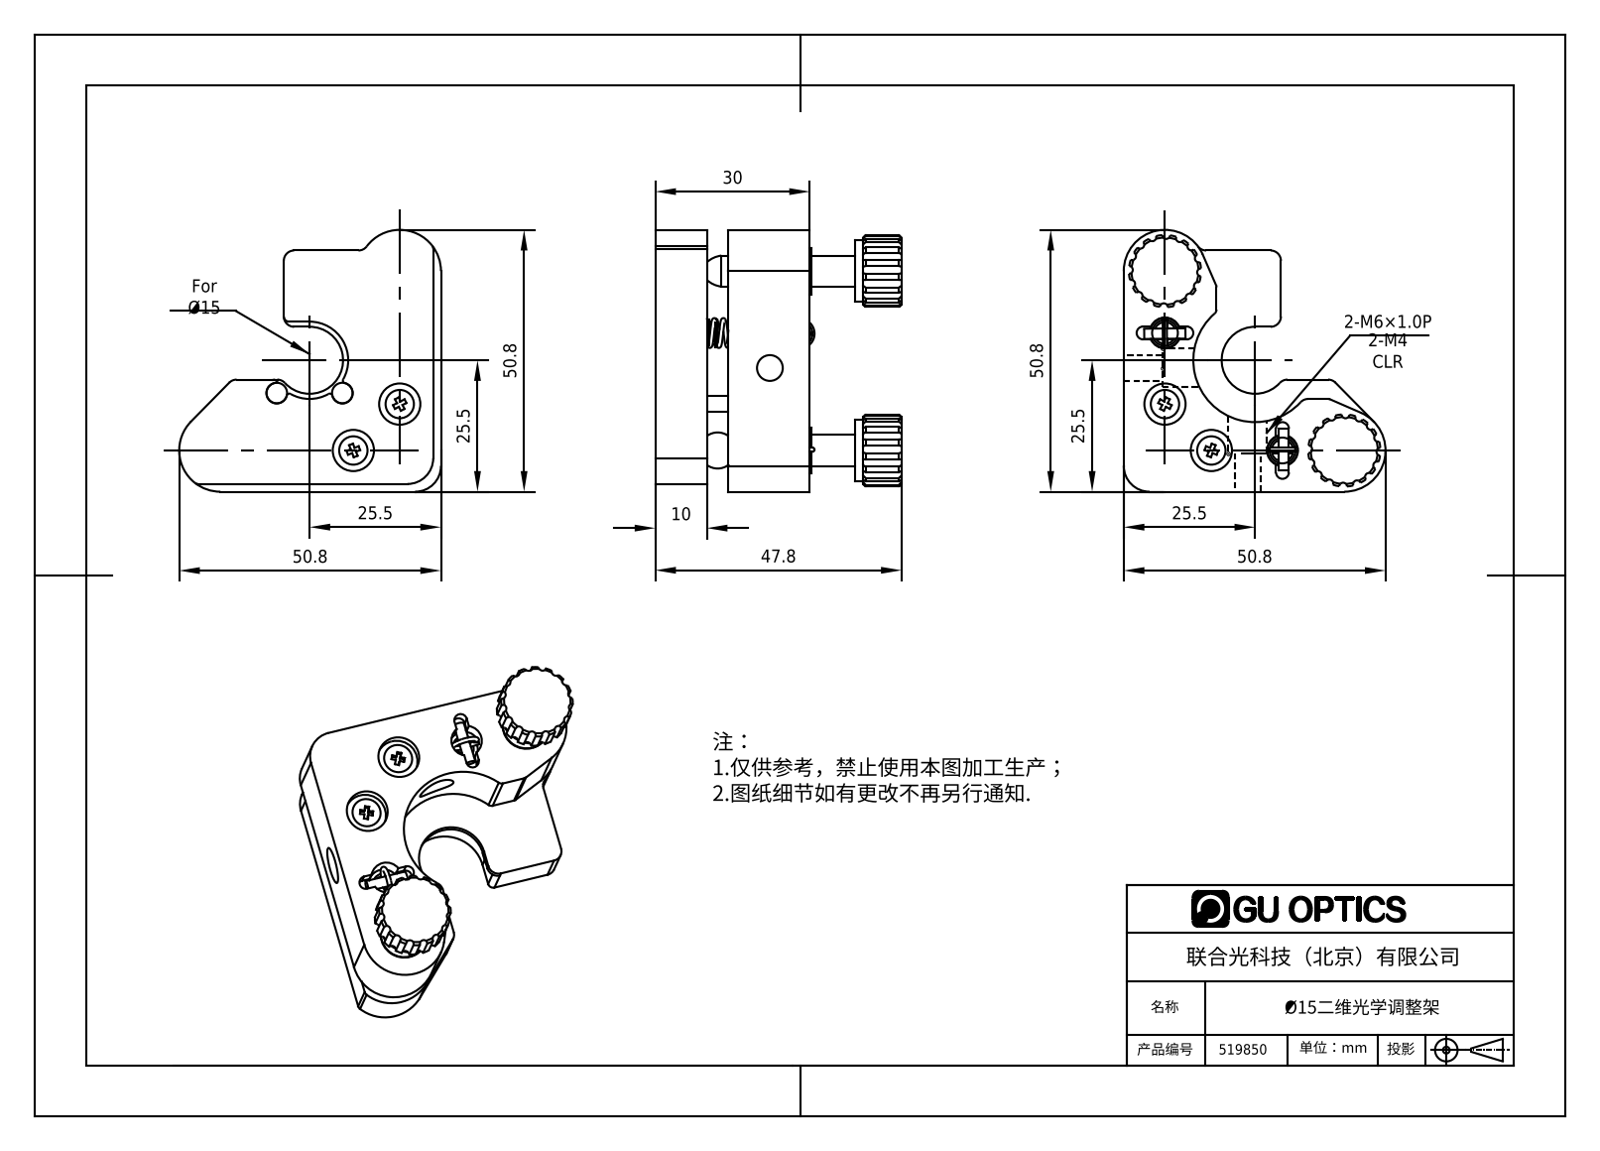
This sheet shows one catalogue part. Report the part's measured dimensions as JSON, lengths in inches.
{"part_name": "519850", "step_written_by": "SolidWorks 2016 (AUTOMOTIVE_DESIGN)", "units": "inches", "bodies": {"solids": 0, "faces": 620, "planar": 206, "cylindrical": 203, "other": 211}, "overall_size": [2, 2, 1.882], "round_holes": [[0.236, 4], [0.315, 4], [0.157, 3], [0.197, 2], [0.295, 2], [0.138, 1]], "round_bosses_or_shafts": [[0.472, 2], [0.354, 2], [0.213, 2], [0.118, 2], [0.079, 2], [0.031, 2], [0.157, 1]], "partial_cylinders_radius": [[0.03, 32], [0.039, 7], [0.079, 6], [0.049, 4], [0.02, 3], [0.197, 2], [0.276, 2], [0.315, 2]], "face_to_face_distances": [0.394, 0.165, 0.559, 0.787, 0.622, 1.181, 0.059, 1.488, 0.701, 1.323], "hole_center_spacings": [0.472, 0.543, 0.965, 1.016, 1.415, 1.638, 0.441, 0.501]}
